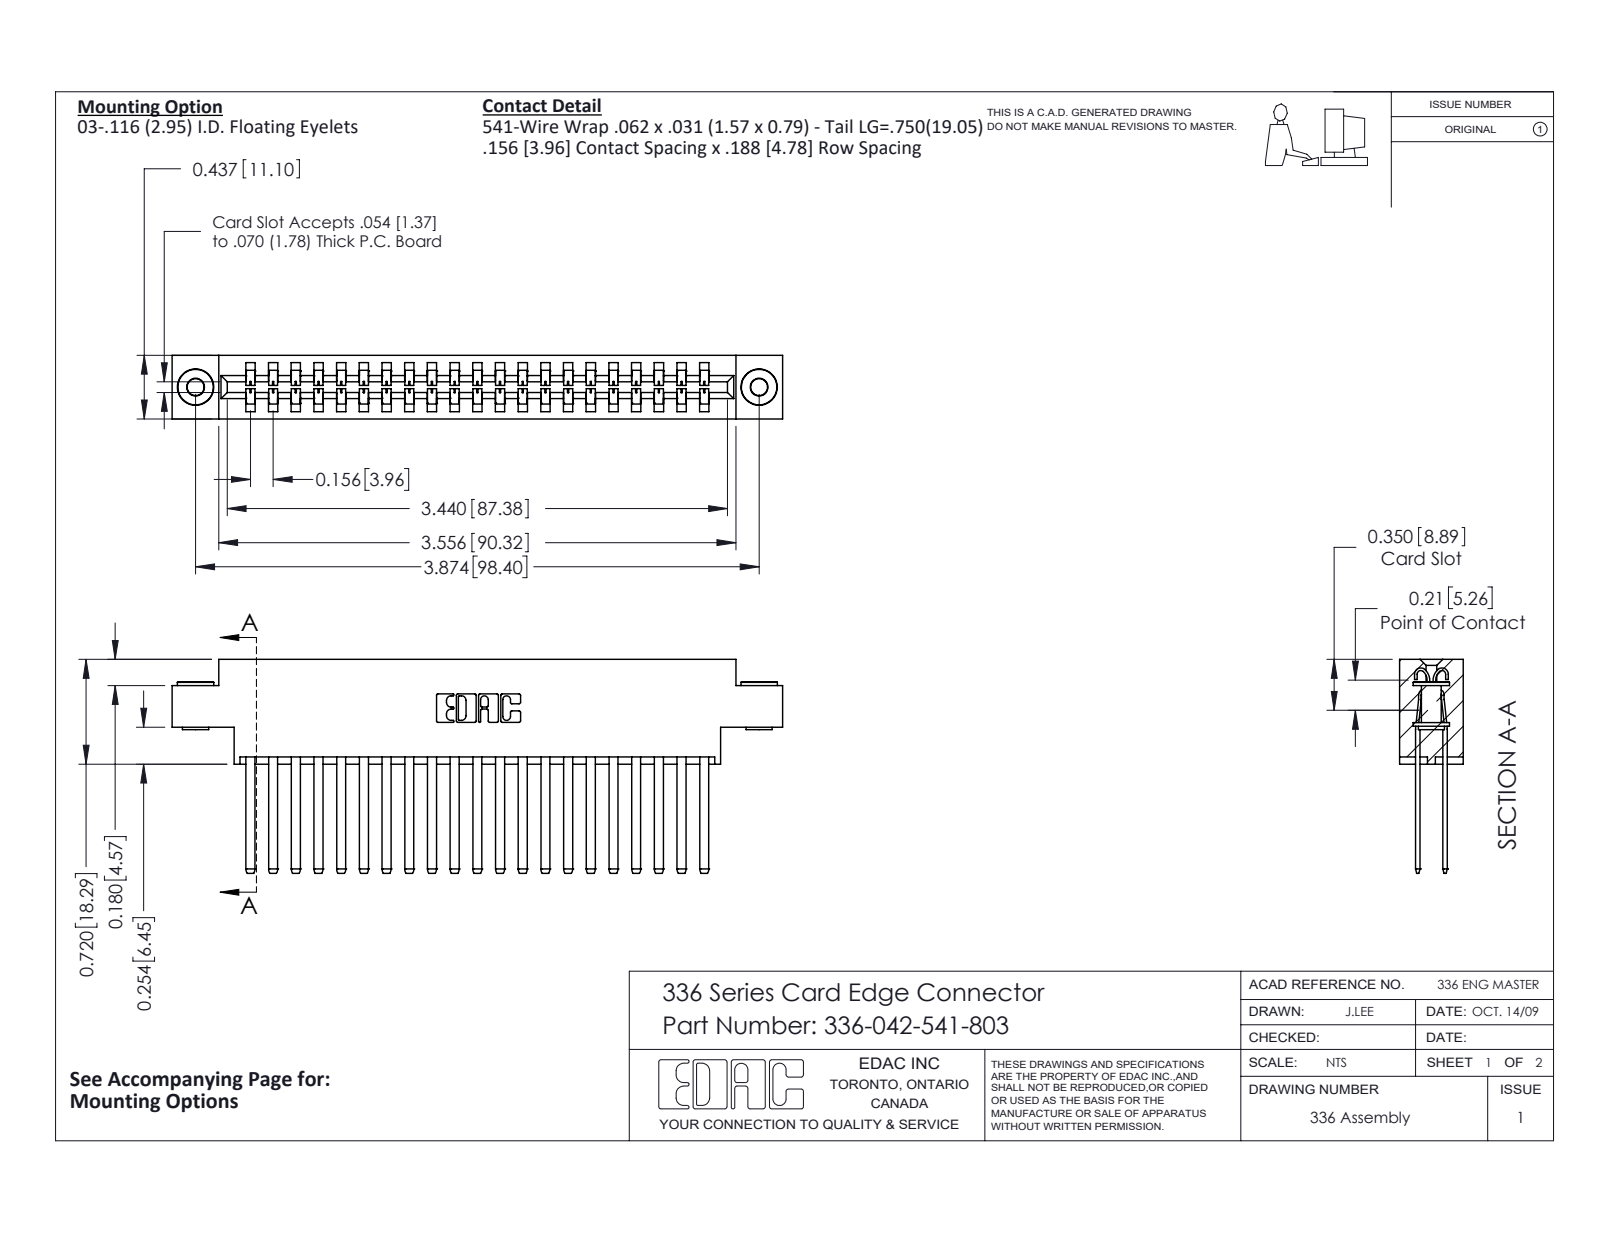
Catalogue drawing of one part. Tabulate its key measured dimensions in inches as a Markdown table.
| quantity | value |
| --- | --- |
| part name | 336 Part_Offset - .156 Dia - TH; 336-042-541-803; 336-290-001_336-290-541; 345-250-002_345-250-002-102 |
| STEP written by | SolidWorks 2020 (CONFIG_CONTROL_DESIGN) |
| units | inches |
| bodies | 45 solids, 1920 faces (1176 planar, 736 cylindrical, 8 other) |
| overall size | 4.197 × 1.47 × 0.437 |
| volume | 0.964 in³ |
| surface area | 31.11 in² |
| round holes (diameter × count) | 0.116 × 2, 0.156 × 2 |
| round bosses / shafts (diameter × count) | 0.25 × 2, 0.18 × 2, 0.136 × 2 |
| partial cylindrical surfaces (radius × count) | 0.004 × 84, 0.056 × 42, 0.01 × 22, 0.007 × 6, 0.031 × 6, 0.022 × 4, 0.04 × 4, 0.026 × 3 |
| main face-to-face distances | 0.188, 0.031, 0.328, 0.14, 0.297, 0.109, 0.437, 0.033, 0.181, 0.256 |
| hole center spacings | 3.874 |
